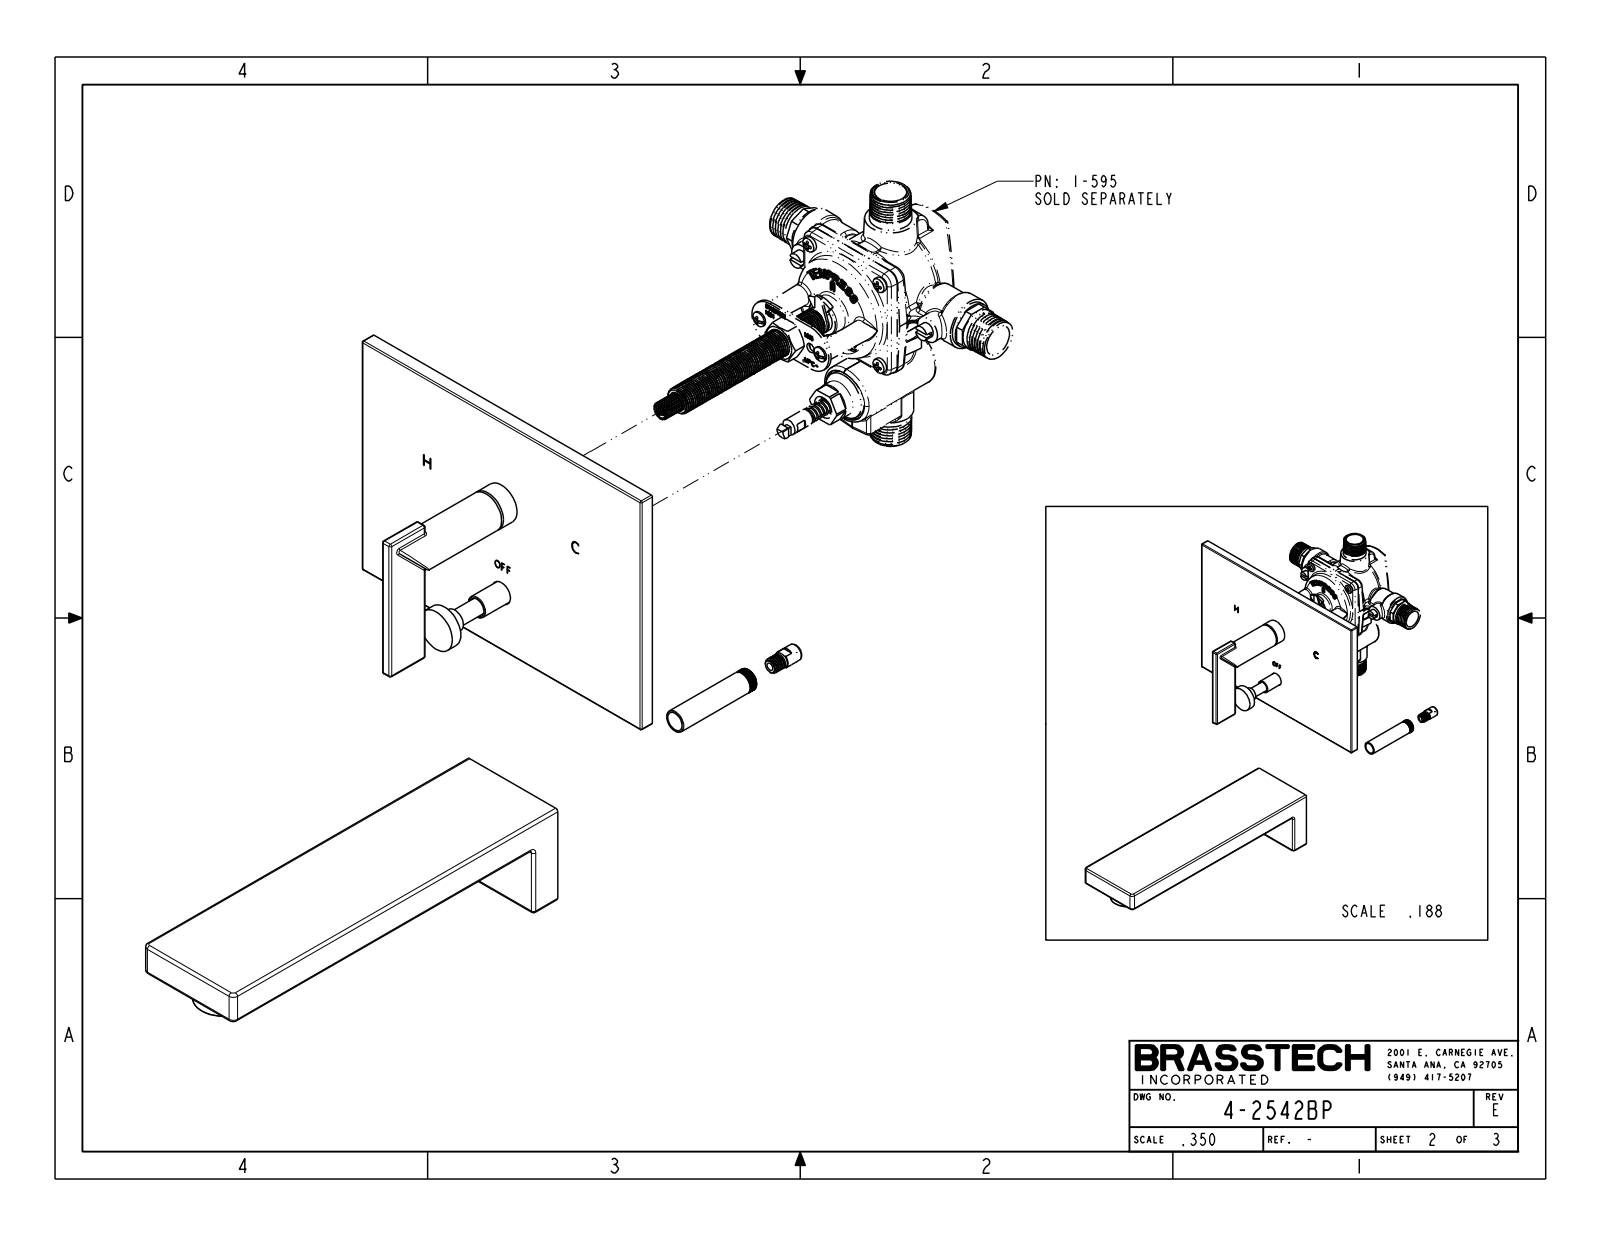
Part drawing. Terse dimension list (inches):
name: 4-2542BP_WEB
written by: PRO/ENGINEER BY PARAMETRIC TECHNOLOGY CORPORATION, 2009300 (CONFIG_CONTROL_DESIGN)
unit: in
bodies: 0 solids, 146 faces (52 planar, 56 cylindrical, 38 other)
size: 11.1 × 9 × 7.75
bosses: 1× ⌀1.25, 1× ⌀0.9, 1× ⌀0.86, 1× ⌀0.68, 1× ⌀0.475, 1× ⌀0.472, 1× ⌀0.354
rounds: 16× R0.04, 11× R0.06, 4× R0.625, 4× R0.875, 2× R0.118, 1× R0.08
face distances: 0.126, 0.67, 0.2, 0.326, 2.5, 1.132, 1.368, 2.625, 3.757, 3.993
